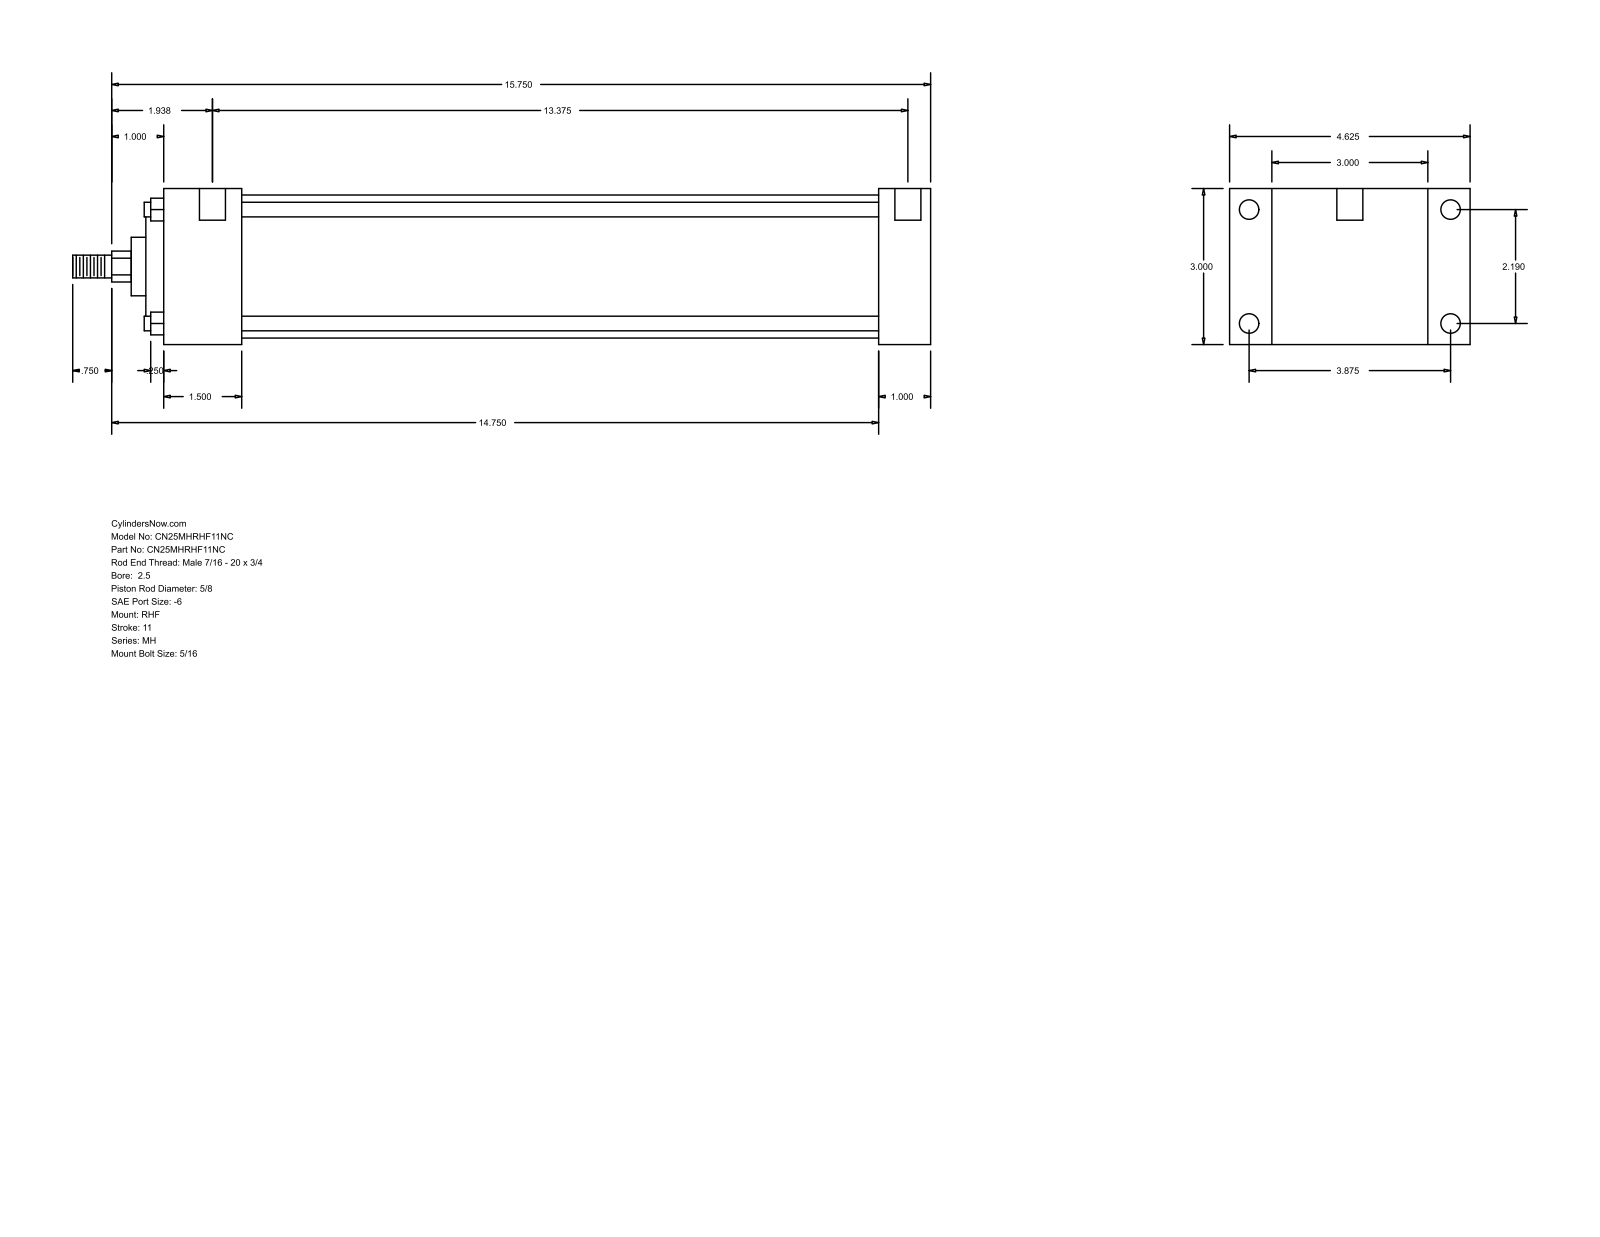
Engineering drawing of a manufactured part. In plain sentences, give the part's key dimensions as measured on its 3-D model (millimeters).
The part is named "MH_RHF__0250_0.625". Its 3-D file was written by "GSSL Pune (CONFIG_CONTROL_DESIGN)". It is 0 solids with 90 faces: 61 planar, 29 cylindrical and 0 other. Overall it measures 419.1 by 117.47 by 76.2 millimeters. Round holes: 4 of diameter 5.56, 4 of diameter 9.53, 2 of diameter 12.7. Round bosses or shafts: 4 of diameter 7.14, 1 of diameter 69.85, 1 of diameter 55.55, 1 of diameter 28.57, 1 of diameter 15.88, 1 of diameter 11.11. Partial cylindrical surfaces (rounded edges, fillets, slot ends): 1 of radius 7.54. The main face-to-face distances are 76.2, 25.4, 20.64, 96.84, 374.65, 349.25, 38.1, 117.48, 311.15, 336.55. The hole center spacings are 55.62, 98.42, 113.05, 347.66, 3.17, 4.76, 339.73, 342.9.
